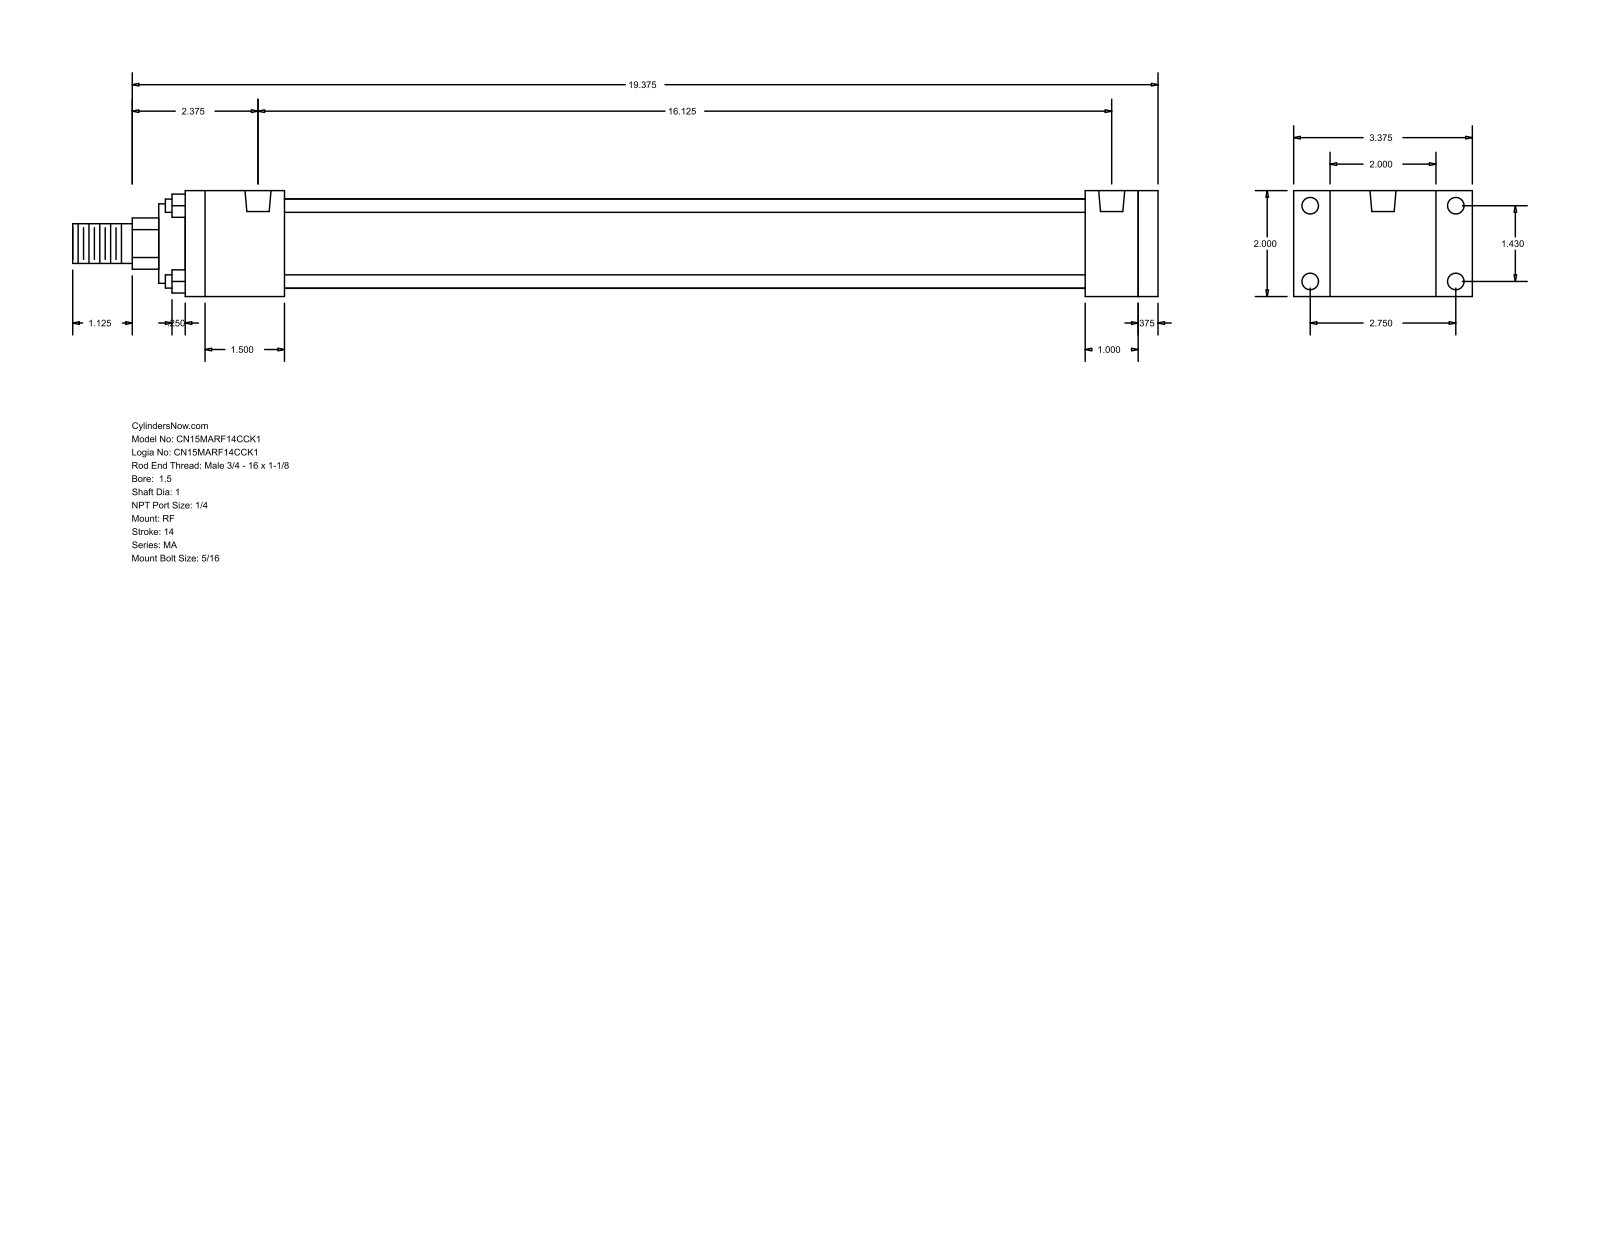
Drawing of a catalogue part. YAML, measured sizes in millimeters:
part_name: "MA_RF__0150_1"
step_written_by: "GSSL Pune (CONFIG_CONTROL_DESIGN)"
units: millimeters
bodies: {solids: 0, faces: 92, planar: 64, cylindrical: 28, other: 0}
overall_size: [520.7, 85.72, 50.8]
round_holes:
  - {diameter: 7.94, count: 8}
  - {diameter: 12.49, count: 2}
round_bosses_or_shafts:
  - {diameter: 6.35, count: 4}
  - {diameter: 42.93, count: 1}
  - {diameter: 38.1, count: 1}
  - {diameter: 25.4, count: 1}
  - {diameter: 19.05, count: 1}
partial_cylinders:
  - {radius: 12.29, count: 1}
face_to_face_distances: [50.8, 9.52, 466.72, 457.2, 25.4, 431.8, 34.92, 47.63, 384.17, 409.57]
hole_center_spacings: [36.32, 69.84, 78.72, 409.57]
